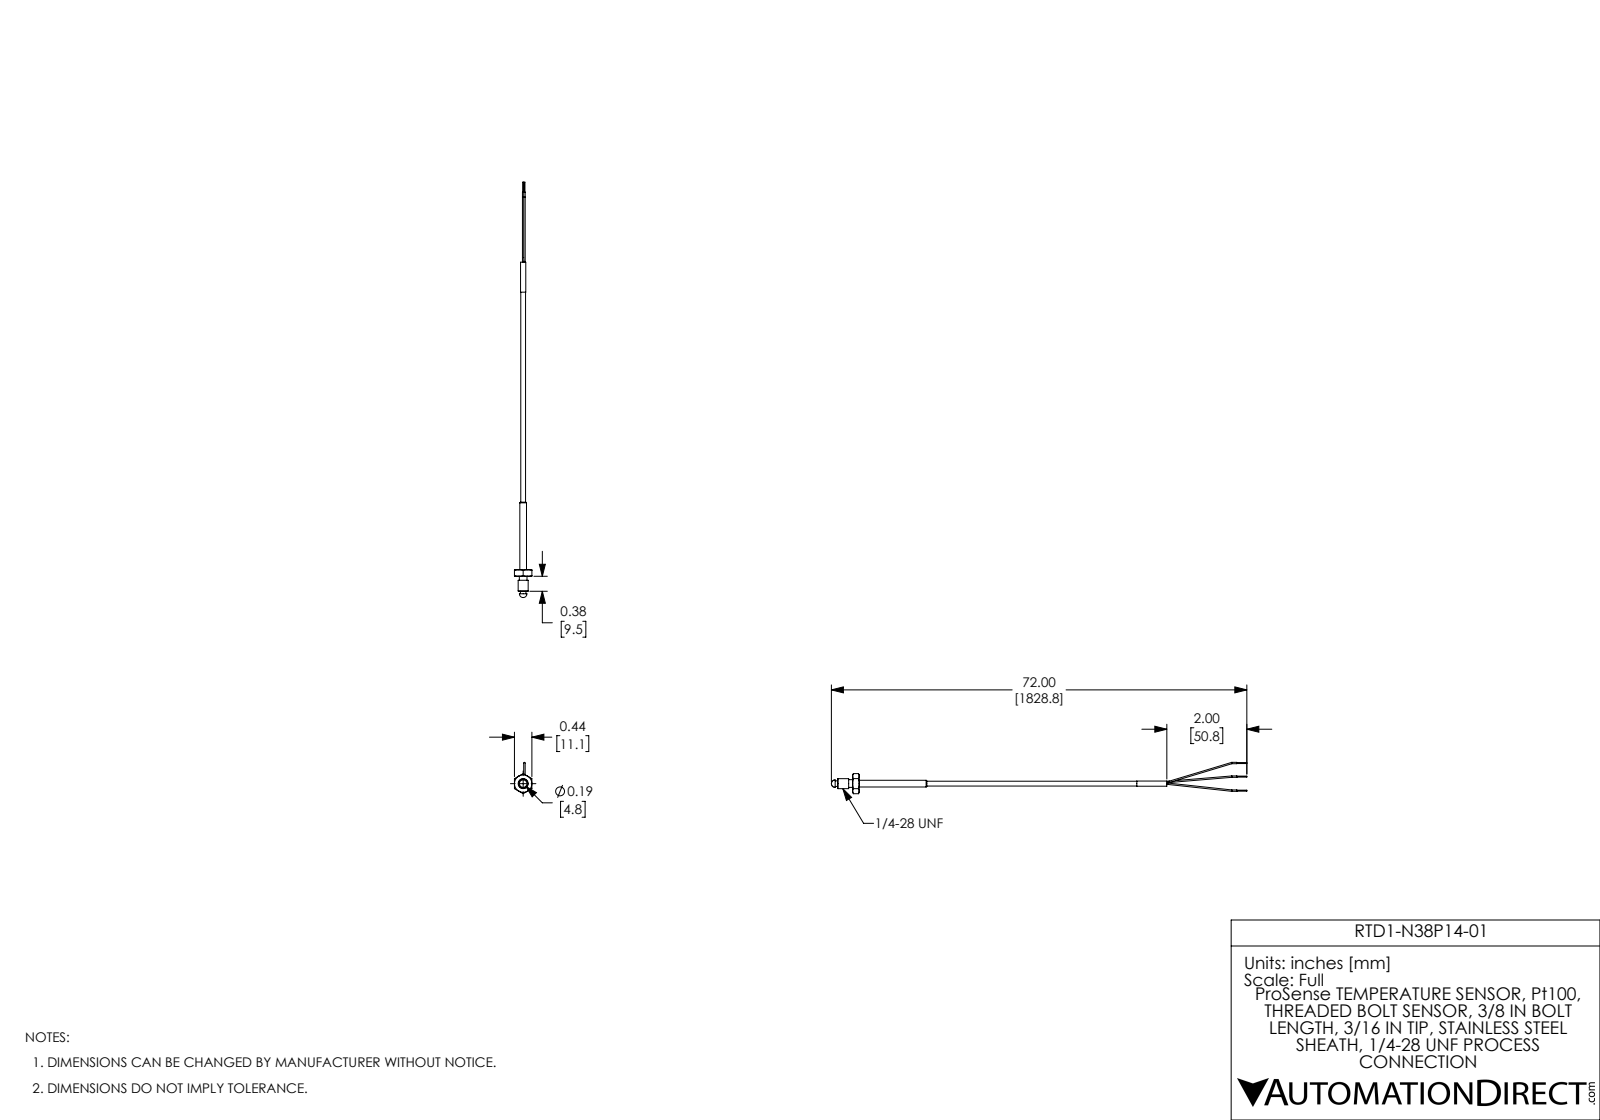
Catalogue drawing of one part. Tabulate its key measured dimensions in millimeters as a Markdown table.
| quantity | value |
| --- | --- |
| part name | RTD1-N38P14-01 |
| STEP written by | SolidWorks 2017 (AUTOMOTIVE_DESIGN) |
| units | millimeters |
| bodies | 4 solids, 78 faces (24 planar, 30 cylindrical, 24 other) |
| overall size | 263.8 × 19.9 × 11.1 |
| volume | 2 650 mm³ |
| surface area | 3 412 mm² |
| round bosses / shafts (diameter × count) | 0.9 × 5, 0.6 × 3, 6.4 × 1, 4.9 × 1, 4.3 × 1, 3.6 × 1, 3.3 × 1, 3 × 1 |
| main face-to-face distances | 4.2, 11, 13.7, 9.5, 42.9, 47.1, 56.6, 49.6, 6.7, 2.5 |
